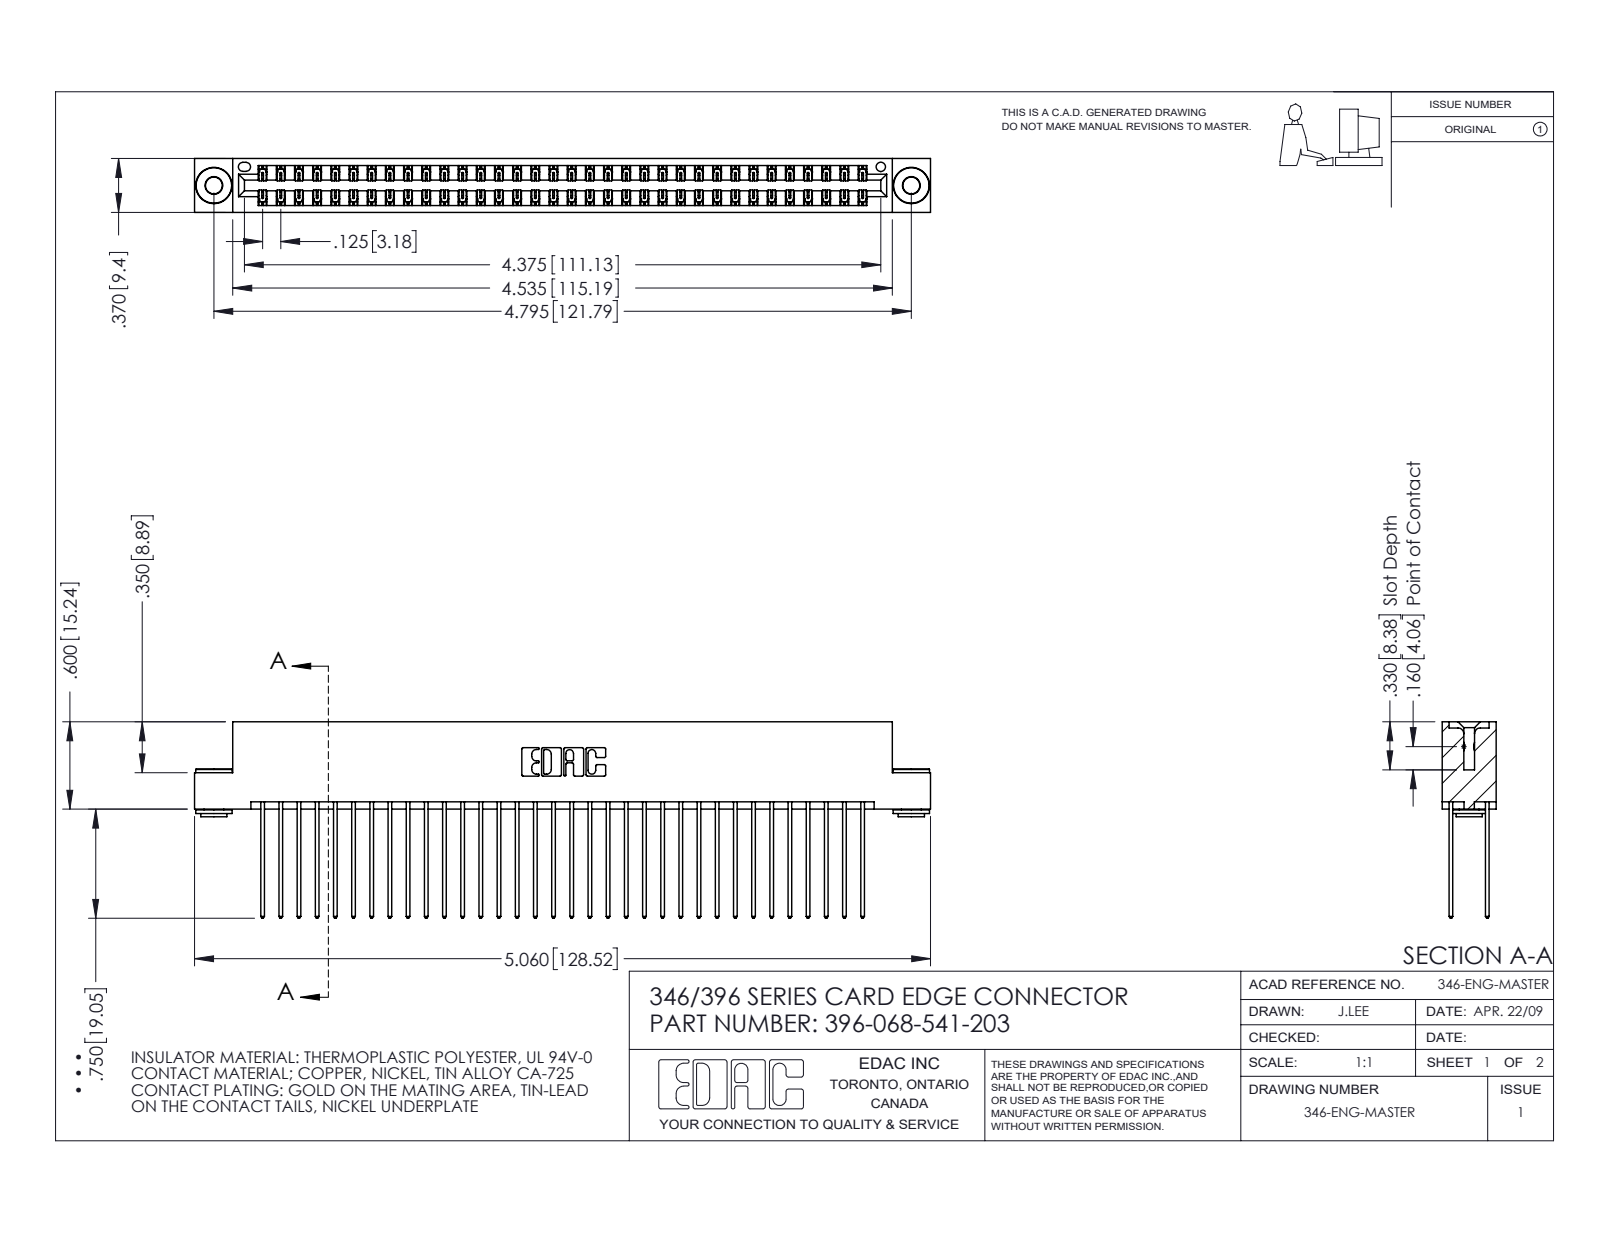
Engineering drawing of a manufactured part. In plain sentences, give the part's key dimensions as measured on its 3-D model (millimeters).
The part is named "396-068-541-203; 346 Part_Flush Mounting Lugs - 0.156 Dia-TH; 345-292-001_345-293-141; 345-250-002_345-250-002-102". Its 3-D file was written by "SolidWorks 2016 (CONFIG_CONTROL_DESIGN)". It is 71 solids with 3696 faces: 2466 planar, 1222 cylindrical and 8 other. Overall it measures 128.5 by 34.3 by 9.4 millimeters. Its volume is 12 900 cubic millimeters and its surface area 19 660 square millimeters. Round holes: 2 of diameter 2.9, 2 of diameter 4, 1 of diameter 1.6. Round bosses or shafts: 2 of diameter 6.4, 2 of diameter 4.6, 2 of diameter 3.5. Partial cylindrical surfaces (rounded edges, fillets, slot ends): 102 of radius 0.2, 68 of radius 0.3, 22 of radius 0.3, 6 of radius 0.2, 6 of radius 0.8, 3 of radius 0.7, 2 of radius 0.4, 2 of radius 0.6. The main face-to-face distances are 1.2, 8.2, 6.4, 0.6, 1.8, 7.6, 9.4, 7, 5.7, 3.8. The hole center spacings are 6.2, 116.5, 121.8.
